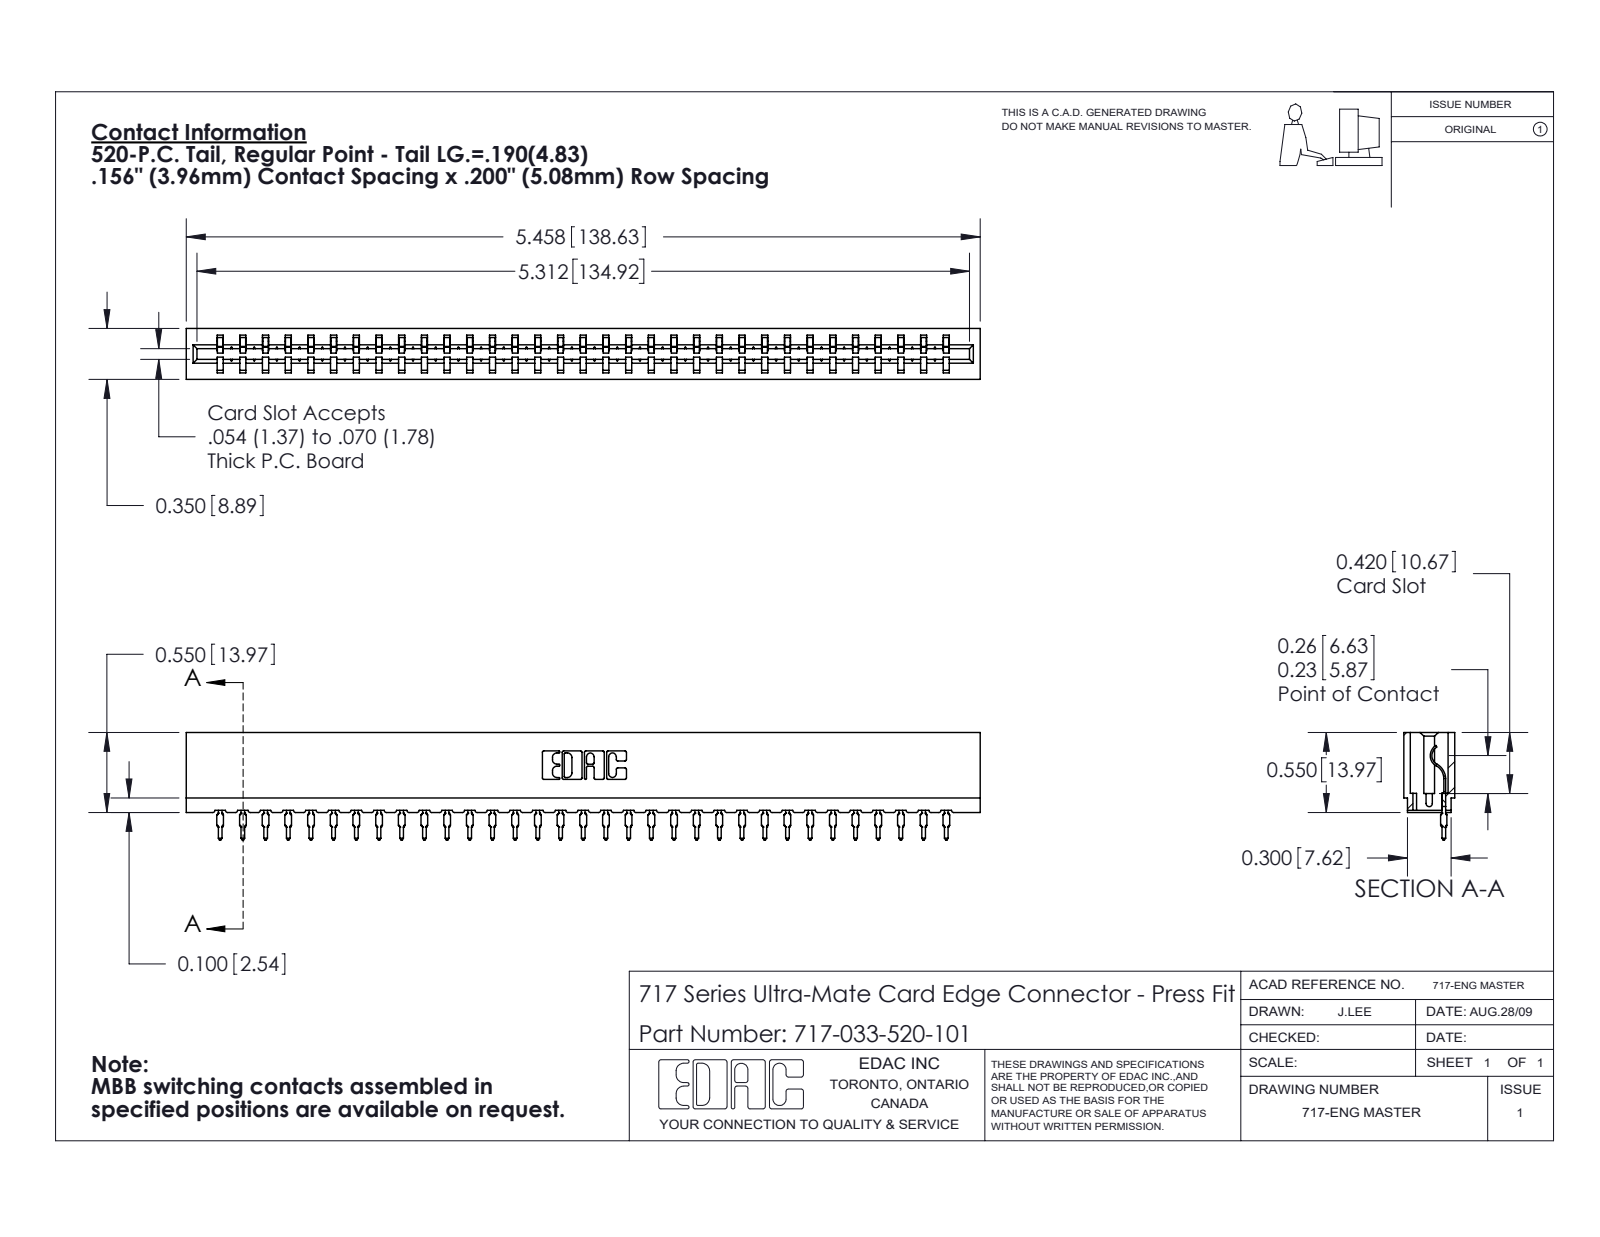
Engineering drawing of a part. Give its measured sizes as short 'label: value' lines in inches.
name: 717 Part_Insulator Option - 06; 745-292-001_520; 717-033-520-101
written by: SolidWorks 2020 (CONFIG_CONTROL_DESIGN)
unit: in
bodies: 34 solids, 3823 faces (2298 planar, 667 cylindrical, 858 other)
size: 5.458 × 0.739 × 0.35
volume: 0.714 in³; area: 24.96 in²
rounds: 66× R0.015, 66× R0.021, 22× R0.01, 6× R0.007, 6× R0.031, 4× R0.005, 4× R0.011, 3× R0.026
face distances: 0.212, 0.138, 0.35, 0.074, 0.045, 0.305, 0.093, 0.167, 0.025, 0.156
